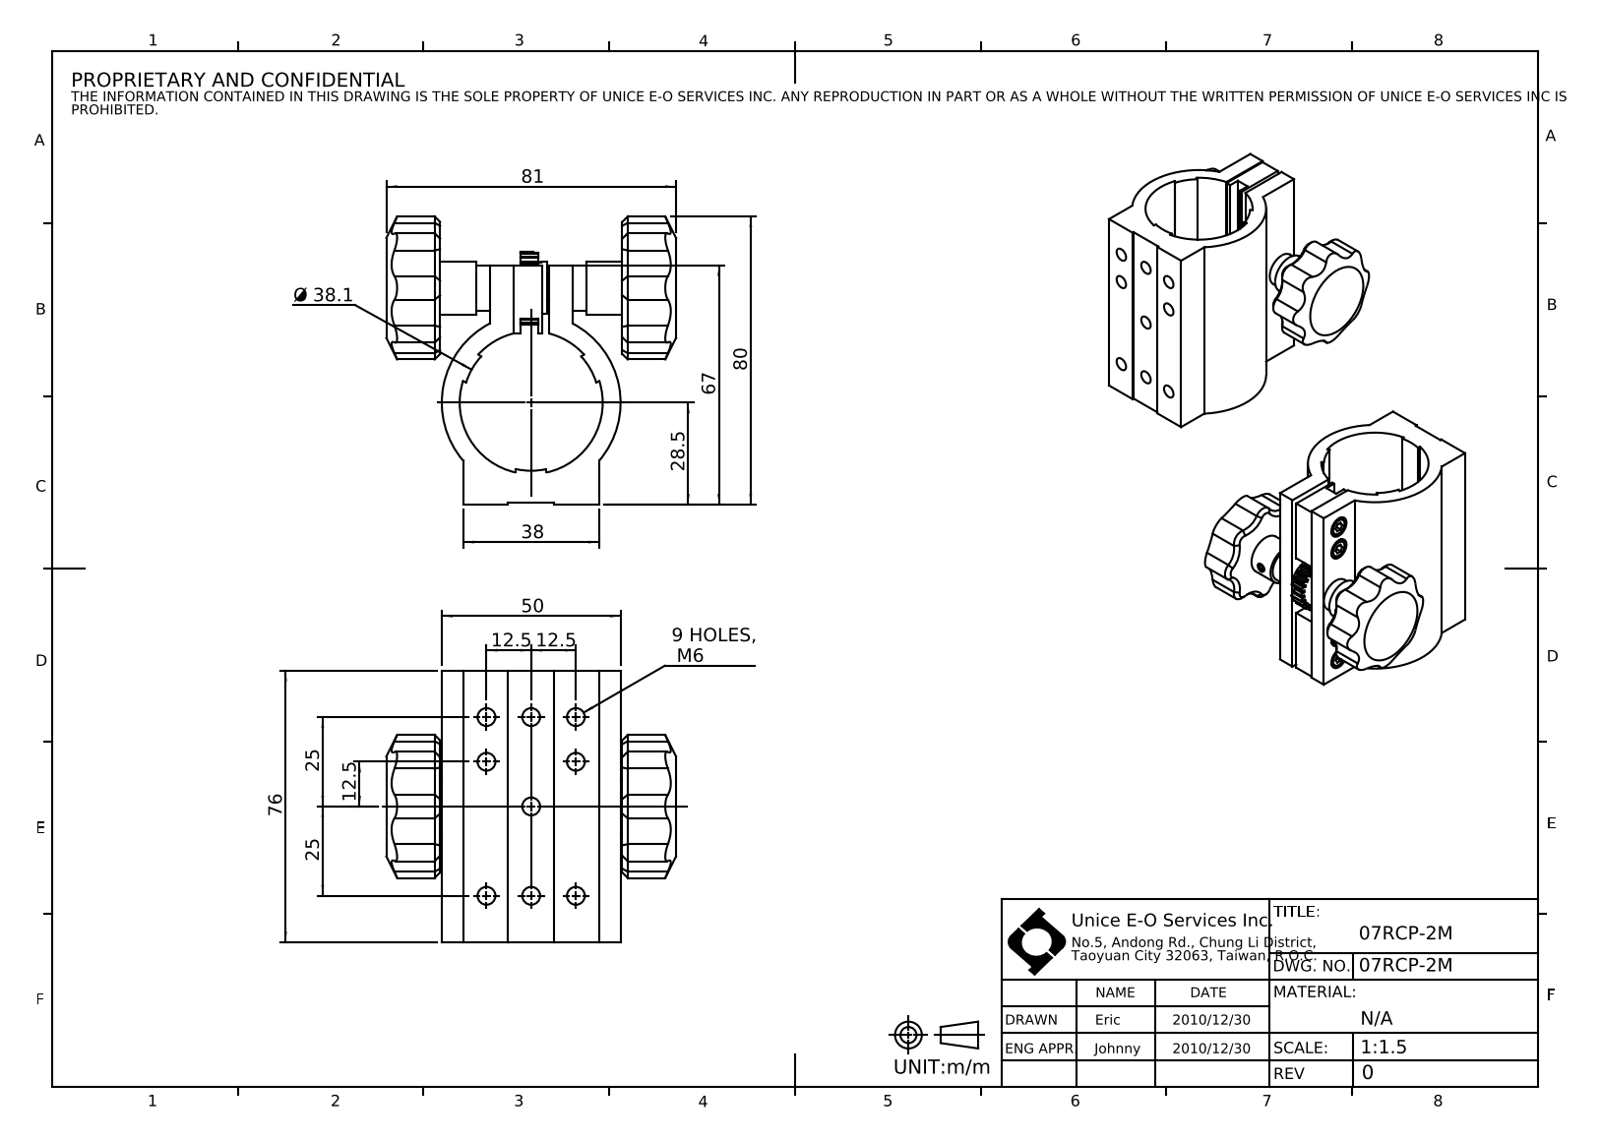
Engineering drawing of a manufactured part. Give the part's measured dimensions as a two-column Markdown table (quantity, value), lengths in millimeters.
| quantity | value |
| --- | --- |
| part name | 07RCP-2M |
| STEP written by | SolidWorks 2016 (AUTOMOTIVE_DESIGN) |
| units | millimeters |
| bodies | 0 solids, 300 faces (124 planar, 118 cylindrical, 58 other) |
| overall size | 81 × 80.6 × 76 |
| round holes (diameter × count) | 5 × 9, 8 × 4, 2.5 × 1 |
| round bosses / shafts (diameter × count) | 7 × 4, 15 × 1, 14.5 × 1, 12.7 × 1 |
| partial cylindrical surfaces (radius × count) | 4 × 8, 7 × 8, 8.25 × 1, 10.15 × 1, 19.05 × 1, 20 × 1, 25 × 1 |
| main face-to-face distances | 6.5, 14, 30.5, 16.5, 7.5, 24, 20.5, 10, 15, 52 |
| hole center spacings | 12.5, 27.95, 25, 50, 17.68, 51.54, 10, 37.5 |
